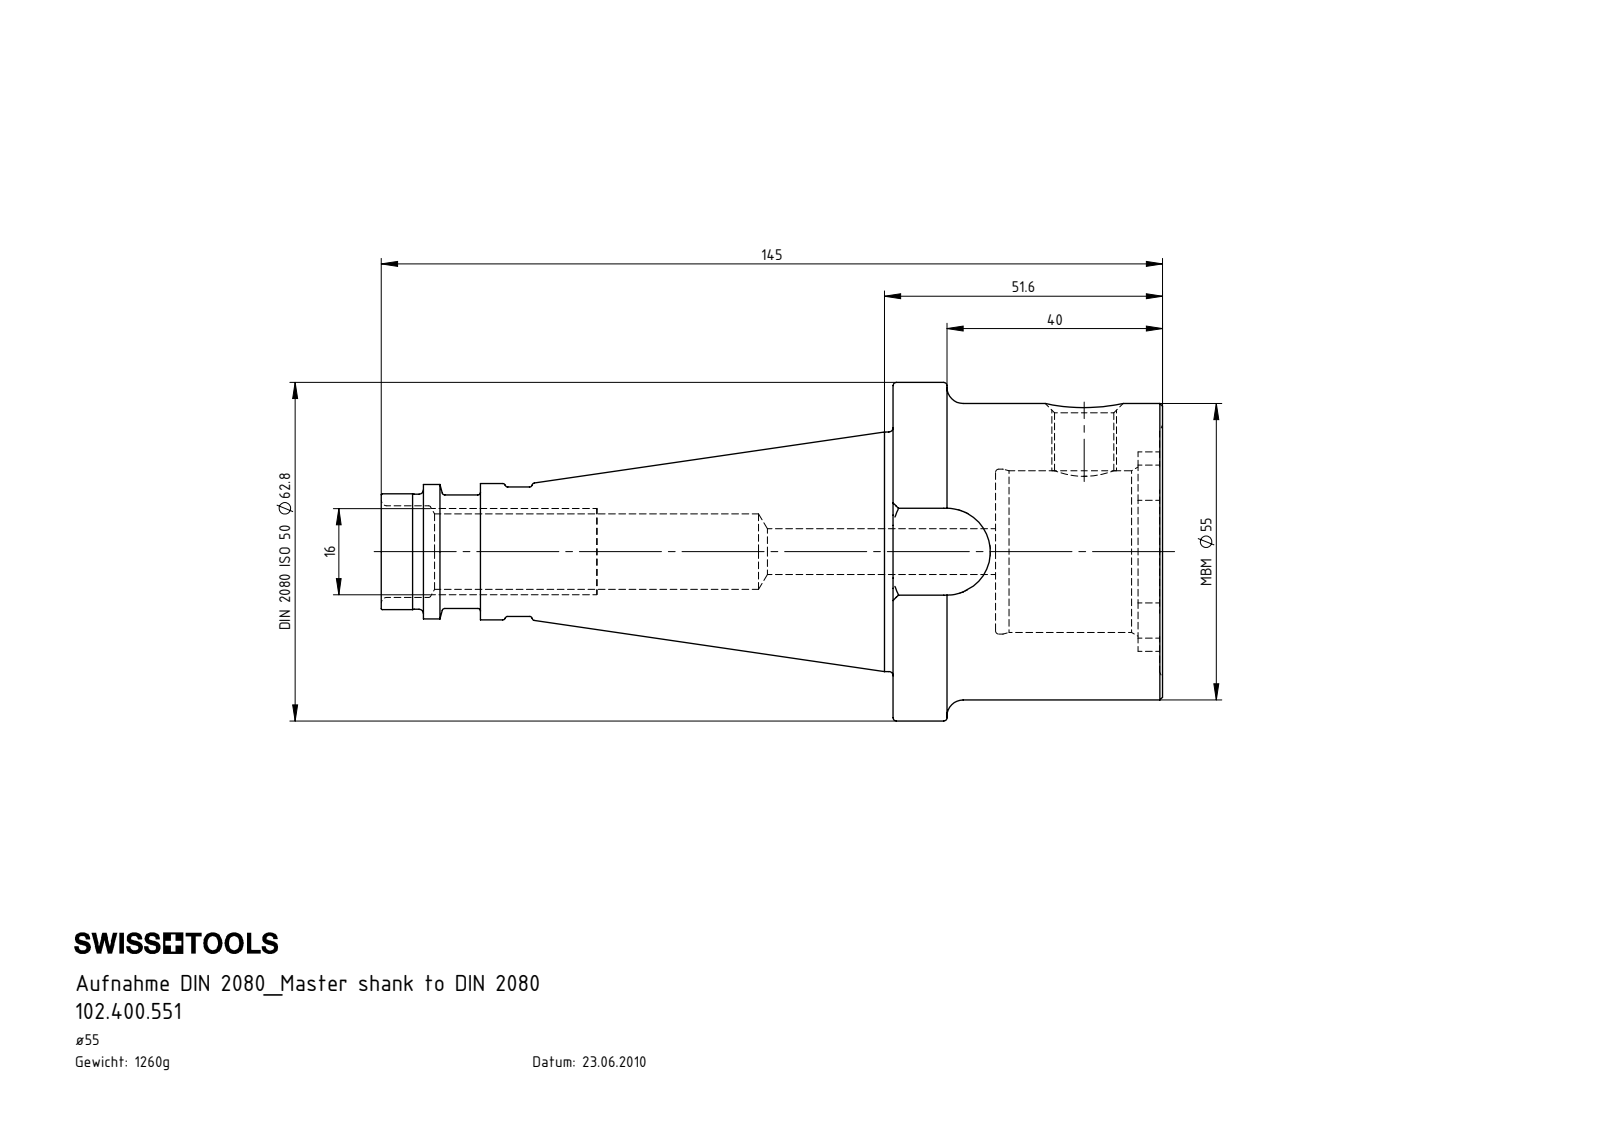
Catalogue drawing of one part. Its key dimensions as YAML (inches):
part_name: "102.400.551"
step_written_by: "SolidWorks 2017 (CONFIG_CONTROL_DESIGN)"
units: inches
bodies: {solids: 1, faces: 137, planar: 30, cylindrical: 52, other: 55}
overall_size: [5.709, 2.472, 2.39]
volume: 9.797
surface_area: 47.83
round_holes:
  - {diameter: 0.335, count: 1}
  - {diameter: 0.433, count: 1}
  - {diameter: 0.551, count: 1}
  - {diameter: 0.669, count: 1}
  - {diameter: 1.181, count: 1}
  - {diameter: 1.205, count: 1}
round_bosses_or_shafts:
  - {diameter: 2.472, count: 1}
  - {diameter: 2.165, count: 1}
  - {diameter: 1.75, count: 1}
  - {diameter: 0.996, count: 1}
  - {diameter: 0.981, count: 1}
  - {diameter: 0.945, count: 1}
  - {diameter: 0.846, count: 1}
  - {diameter: 0.841, count: 1}
partial_cylinders:
  - {radius: 0.063, count: 8}
  - {radius: 0.205, count: 4}
  - {radius: 0.317, count: 1}
  - {radius: 0.728, count: 1}
  - {radius: 0.837, count: 1}
face_to_face_distances: [0.748, 1.969, 1.22, 1.789, 1.041, 0.179, 1.947, 1.199, 0.157, 0.022]
